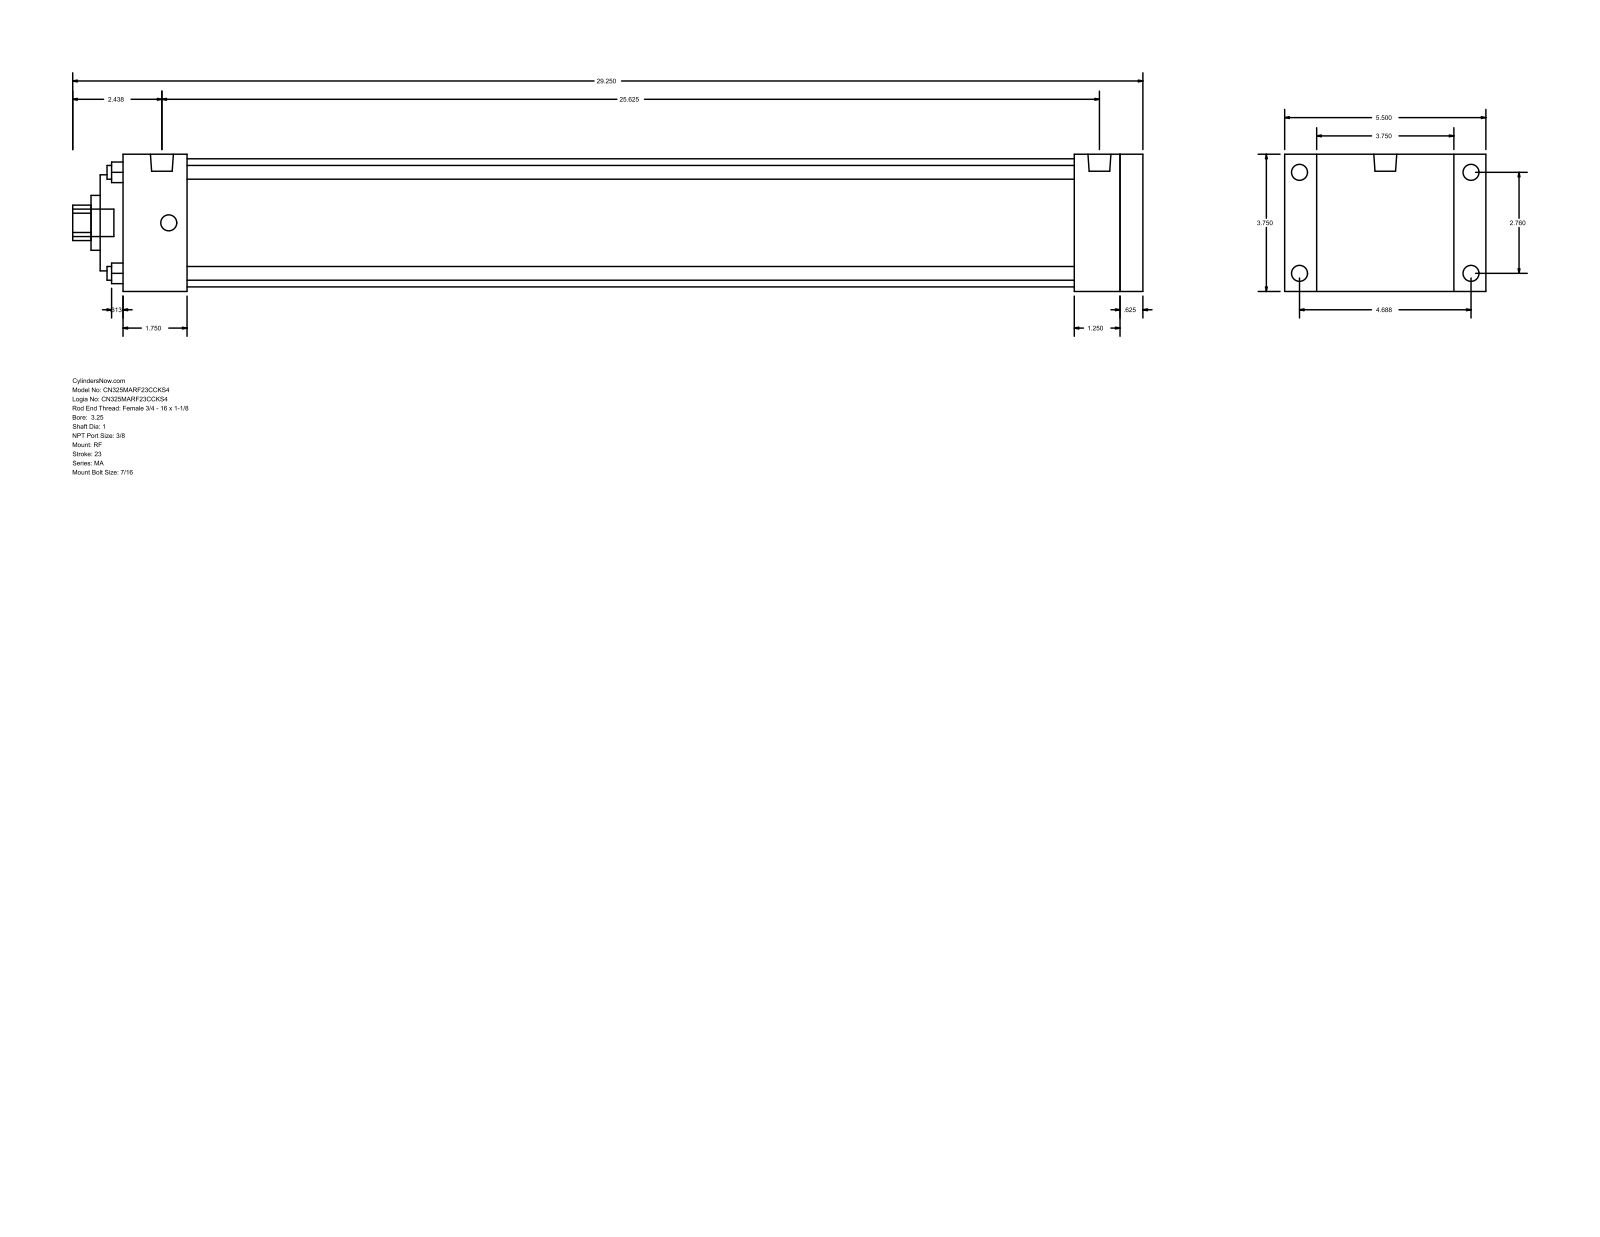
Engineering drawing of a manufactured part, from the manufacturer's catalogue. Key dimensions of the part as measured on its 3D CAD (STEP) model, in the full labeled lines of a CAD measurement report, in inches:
Part name (STEP PRODUCT): MA_RF__0325_1
STEP written by: GSSL Pune (CONFIG_CONTROL_DESIGN)
Units: inches
Bodies: 0 solids, 94 faces (65 planar, 29 cylindrical, 0 other)
Overall size (bounding box): 29.25 × 5.5 × 3.75
Round holes (diameter × count): ⌀0.375 ×4, ⌀1 ×1, ⌀1.5 ×1, ⌀2.625 ×1, ⌀3.5 ×1
Round bosses / shafts (diameter × count): ⌀0.437 ×8, ⌀0.627 ×2, ⌀0.75 ×1
Partial cylindrical surfaces — rounded edges, fillets, slot ends (radius × count): R0.484 ×1
Main face-to-face distances: 3.75, 27.875, 0.625, 27.25, 0.875, 4.625, 26, 1.25, 1.875, 1.75
Hole centre spacings: 1.952, 2.76, 3.903
